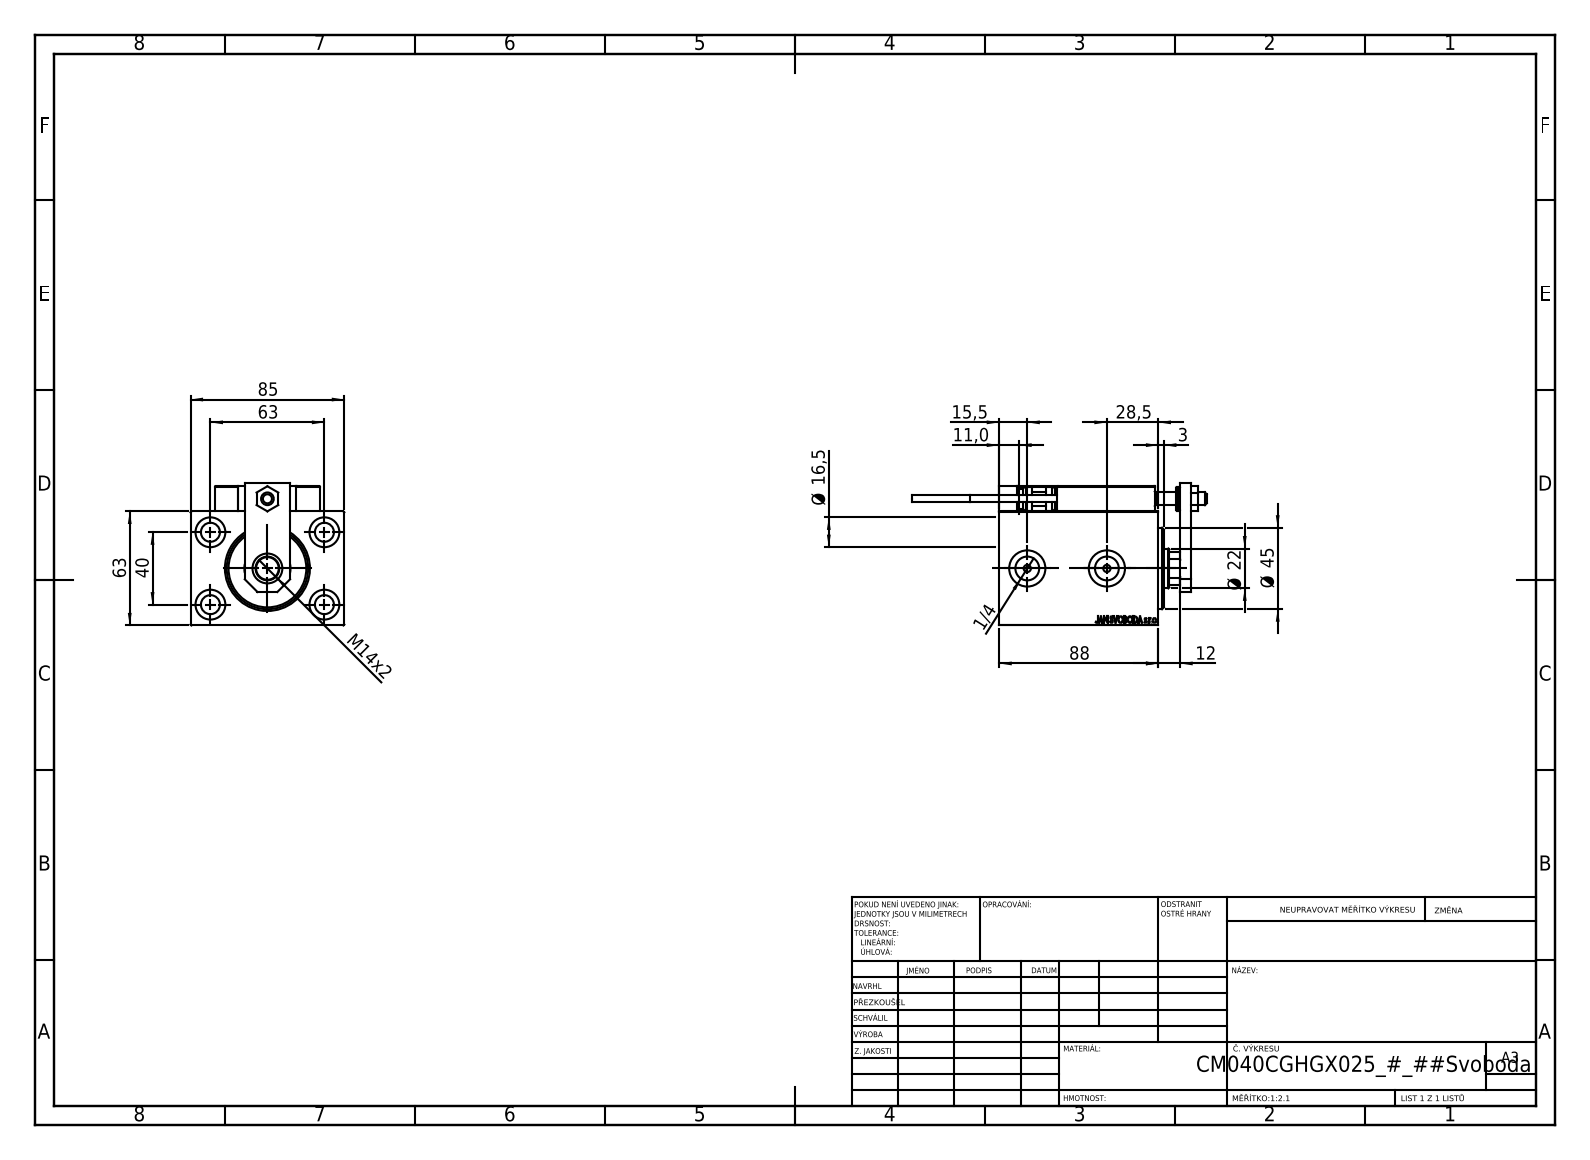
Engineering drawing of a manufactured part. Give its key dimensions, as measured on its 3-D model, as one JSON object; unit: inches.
{"part_name": "NUT_D12; SWITCH DIM B,W; Block; ALLEN BOLT D8 (+7 more)", "step_written_by": "SolidWorks 2019 (CONFIG_CONTROL_DESIGN)", "units": "inches", "bodies": {"solids": 23, "faces": 1282, "planar": 560, "cylindrical": 188, "other": 534}, "overall_size": [6.406, 3.346, 3.091], "volume_in3": 27.91, "surface_area_in2": 157.9, "round_holes": [[0.157, 6], [0.315, 5], [0.65, 5], [0.126, 4], [0.413, 4], [0.197, 2], [0.518, 2], [0.787, 2], [0.276, 1], [0.492, 1], [0.866, 1], [1.004, 1]], "round_bosses_or_shafts": [[0.197, 2], [0.15, 2], [0.512, 1], [0.433, 1]], "partial_cylinders_radius": [[0.012, 30], [0.118, 2], [0.413, 1]], "face_to_face_distances": [2.48, 0.472, 3.346, 2.992, 3.465, 0.551, 3.031, 0.984, 0.591, 0.709], "hole_center_spacings": [1.469, 0.448, 0.787, 1.165, 1.169, 1.42, 1.438, 1.575]}
